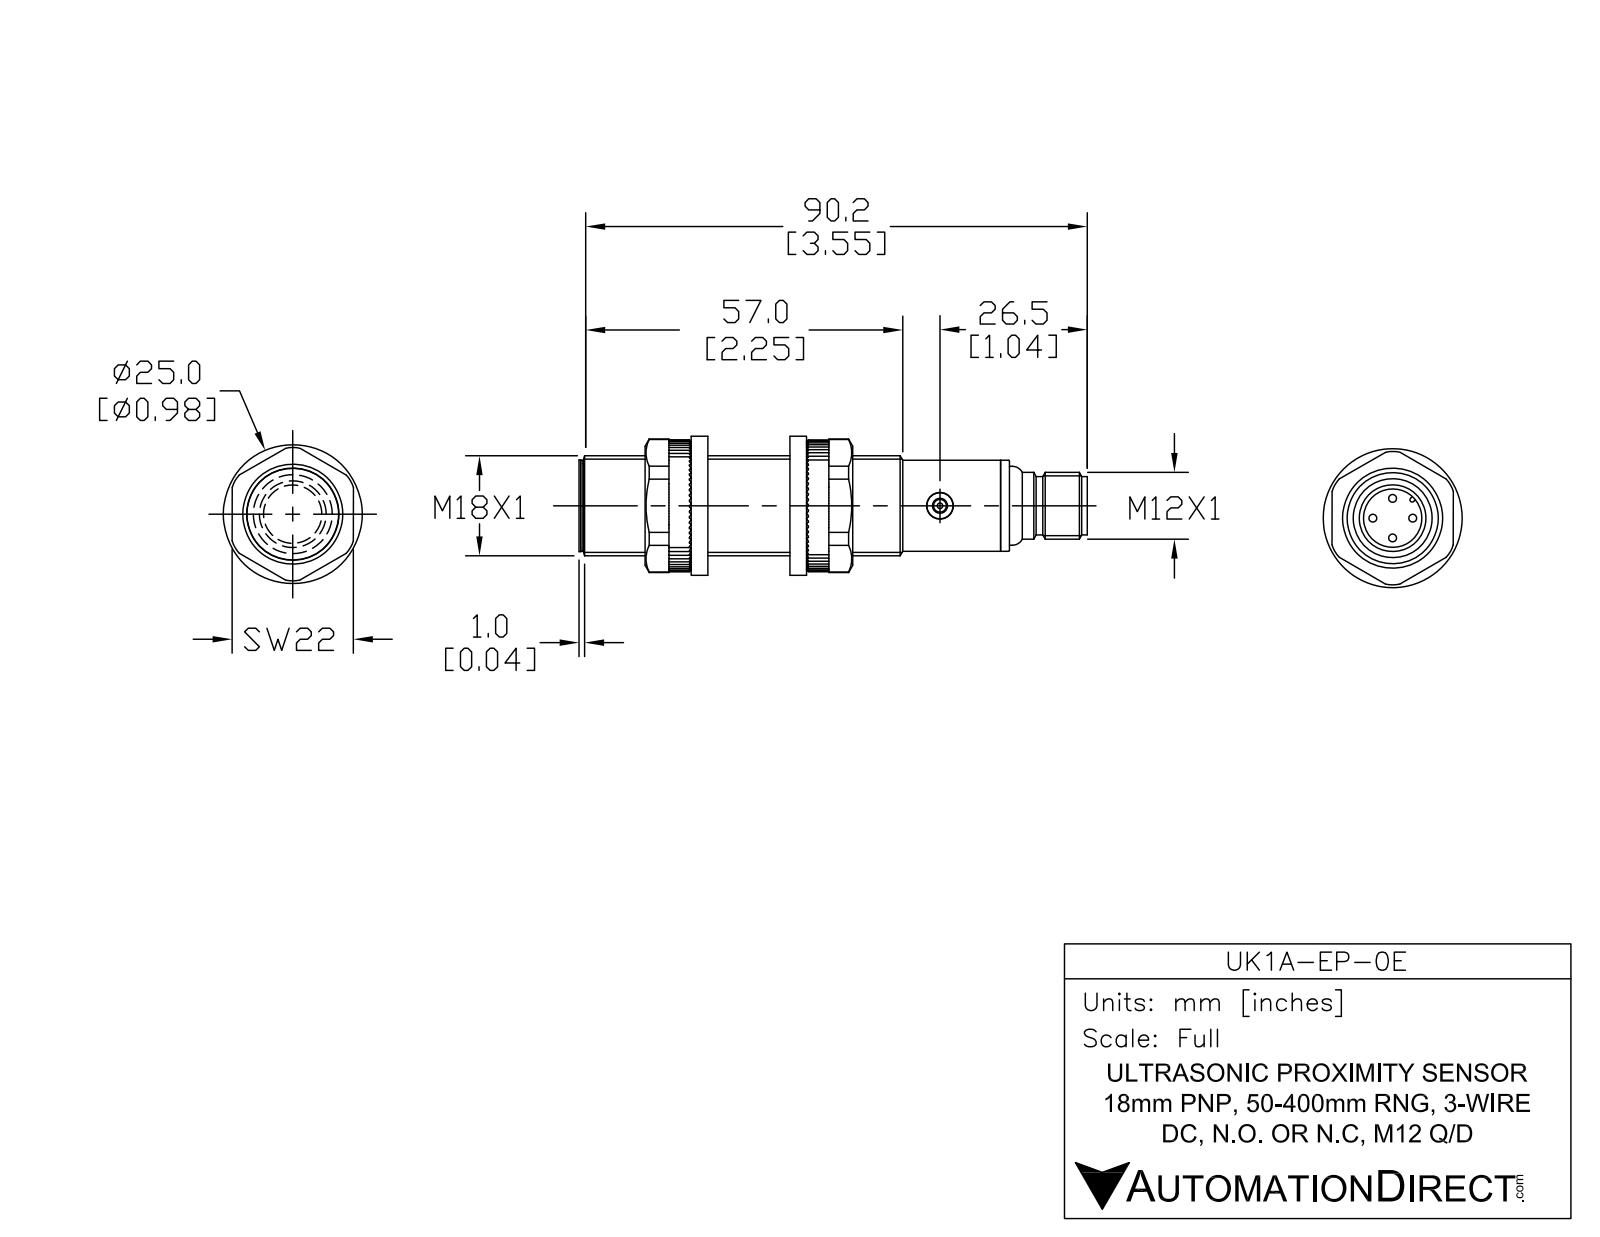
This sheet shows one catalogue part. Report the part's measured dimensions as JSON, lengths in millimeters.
{"part_name": "UK1A-EP-0E", "step_written_by": "SolidWorks 2017 (AUTOMOTIVE_DESIGN)", "units": "millimeters", "bodies": {"solids": 6, "faces": 106, "planar": 21, "cylindrical": 48, "other": 37}, "overall_size": [91.6, 18, 18], "volume_mm3": 19700, "surface_area_mm2": 6890, "round_holes": [[2.7, 1], [4.7, 1], [7, 1], [8.3, 1], [9.5, 1]], "round_bosses_or_shafts": [[1, 4], [18, 1], [16.6, 1], [16.4, 1], [15.8, 1], [14.2, 1], [12, 1], [10.5, 1]], "partial_cylinders_radius": [[0.6, 1]], "face_to_face_distances": [75.1, 1, 76.1, 0.9, 76, 1.1, 4, 77.6, 77.5, 76.6]}
